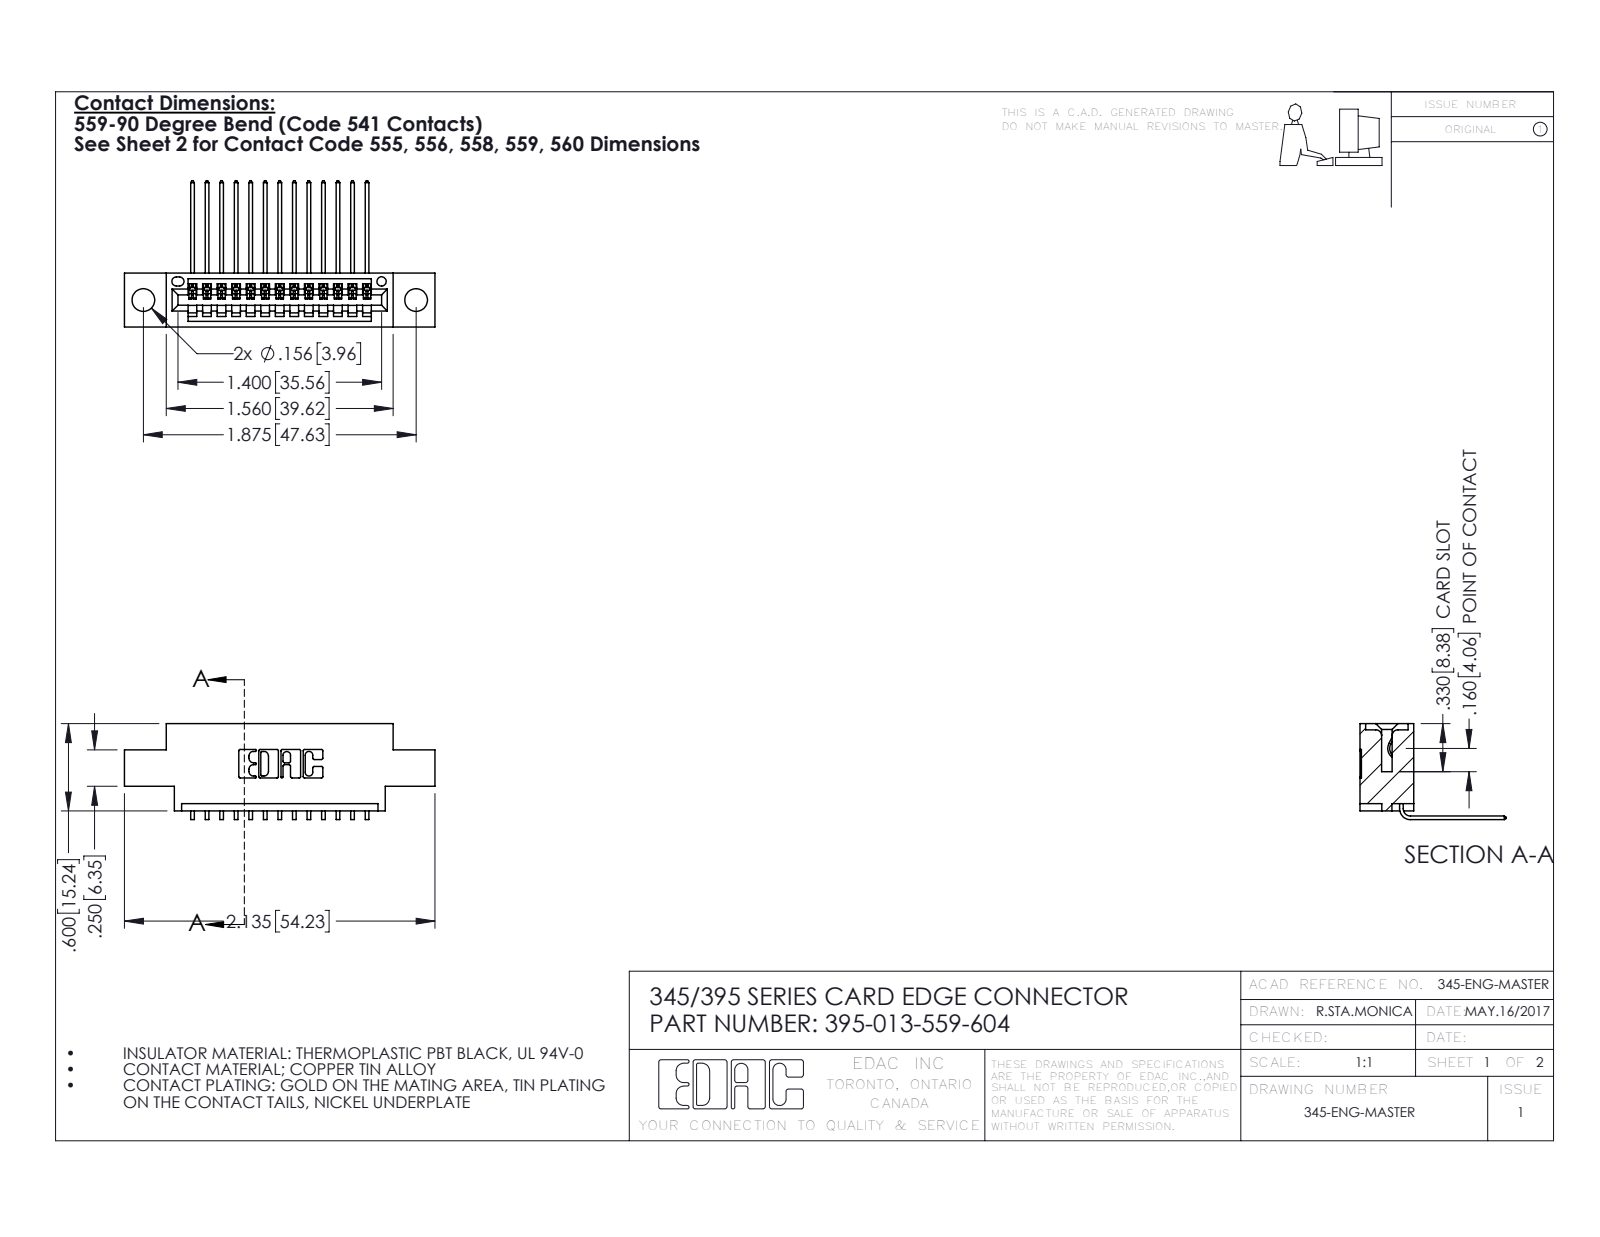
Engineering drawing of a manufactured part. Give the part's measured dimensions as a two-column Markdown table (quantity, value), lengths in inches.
| quantity | value |
| --- | --- |
| part name | 395-013-559-604; 345 Part_0.170 Offset - 0.156 Dia-TH; 345-292-001_558 559 Tail - 1 |
| STEP written by | SolidWorks 2016 (CONFIG_CONTROL_DESIGN) |
| units | inches |
| bodies | 14 solids, 910 faces (630 planar, 280 cylindrical, 0 other) |
| overall size | 2.135 × 1.005 × 0.659 |
| volume | 0.29 in³ |
| surface area | 9.478 in² |
| round holes (diameter × count) | 0.156 × 2, 0.064 × 1 |
| partial cylindrical surfaces (radius × count) | 0.006 × 26, 0.01 × 22, 0.007 × 6, 0.031 × 6, 0.026 × 3, 0.031 × 2, 0.04 × 2, 0.014 × 1 |
| main face-to-face distances | 0.37, 0.072, 0.298, 0.2, 0.098, 0.272, 0.025, 0.1, 0.225, 0.15 |
| hole center spacings | 0.27, 1.643, 1.875 |
